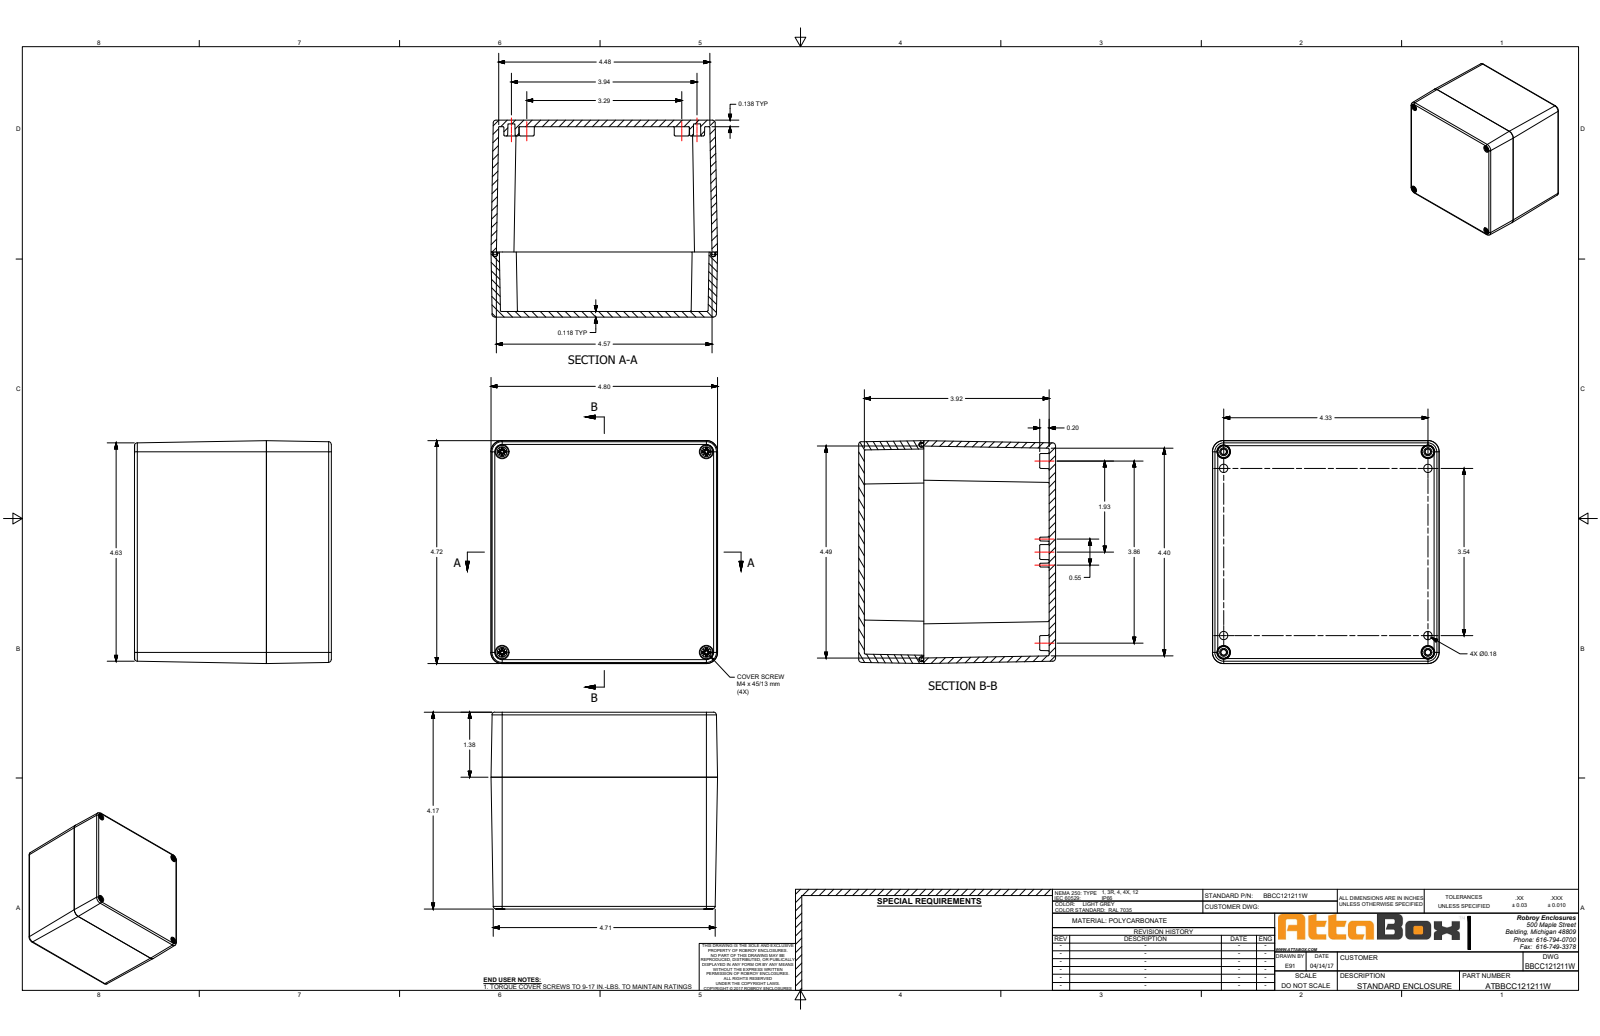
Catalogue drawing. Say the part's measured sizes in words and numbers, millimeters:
The part is named "BBCC121211W". Its 3-D file was written by "SolidWorks 2018 (AUTOMOTIVE_DESIGN)". It is 11 solids with 1669 faces: 611 planar, 440 cylindrical and 618 other. Overall it measures 122 by 120 by 106 millimeters. Its volume is 279 900 cubic millimeters and its surface area 183 000 square millimeters. Round holes: 8 of diameter 4.5, 4 of diameter 3.3, 4 of diameter 4.8, 4 of diameter 5.1, 4 of diameter 7, 4 of diameter 7.3, 4 of diameter 7.5. Round bosses or shafts: 4 of diameter 6.8, 4 of diameter 4.4, 4 of diameter 4, 4 of diameter 3.3. Partial cylindrical surfaces (rounded edges, fillets, slot ends): 48 of radius 1, 40 of radius 0.5, 12 of radius 5, 8 of radius 1.5, 8 of radius 2.5, 4 of radius 2.6, 4 of radius 3.1, 4 of radius 3.3. The main face-to-face distances are 2.9, 106, 3.5, 103, 3, 99.5, 102.5, 4.5, 120, 117. The hole center spacings are 9, 99, 110, 110.4, 148, 90, 108, 142.1.
